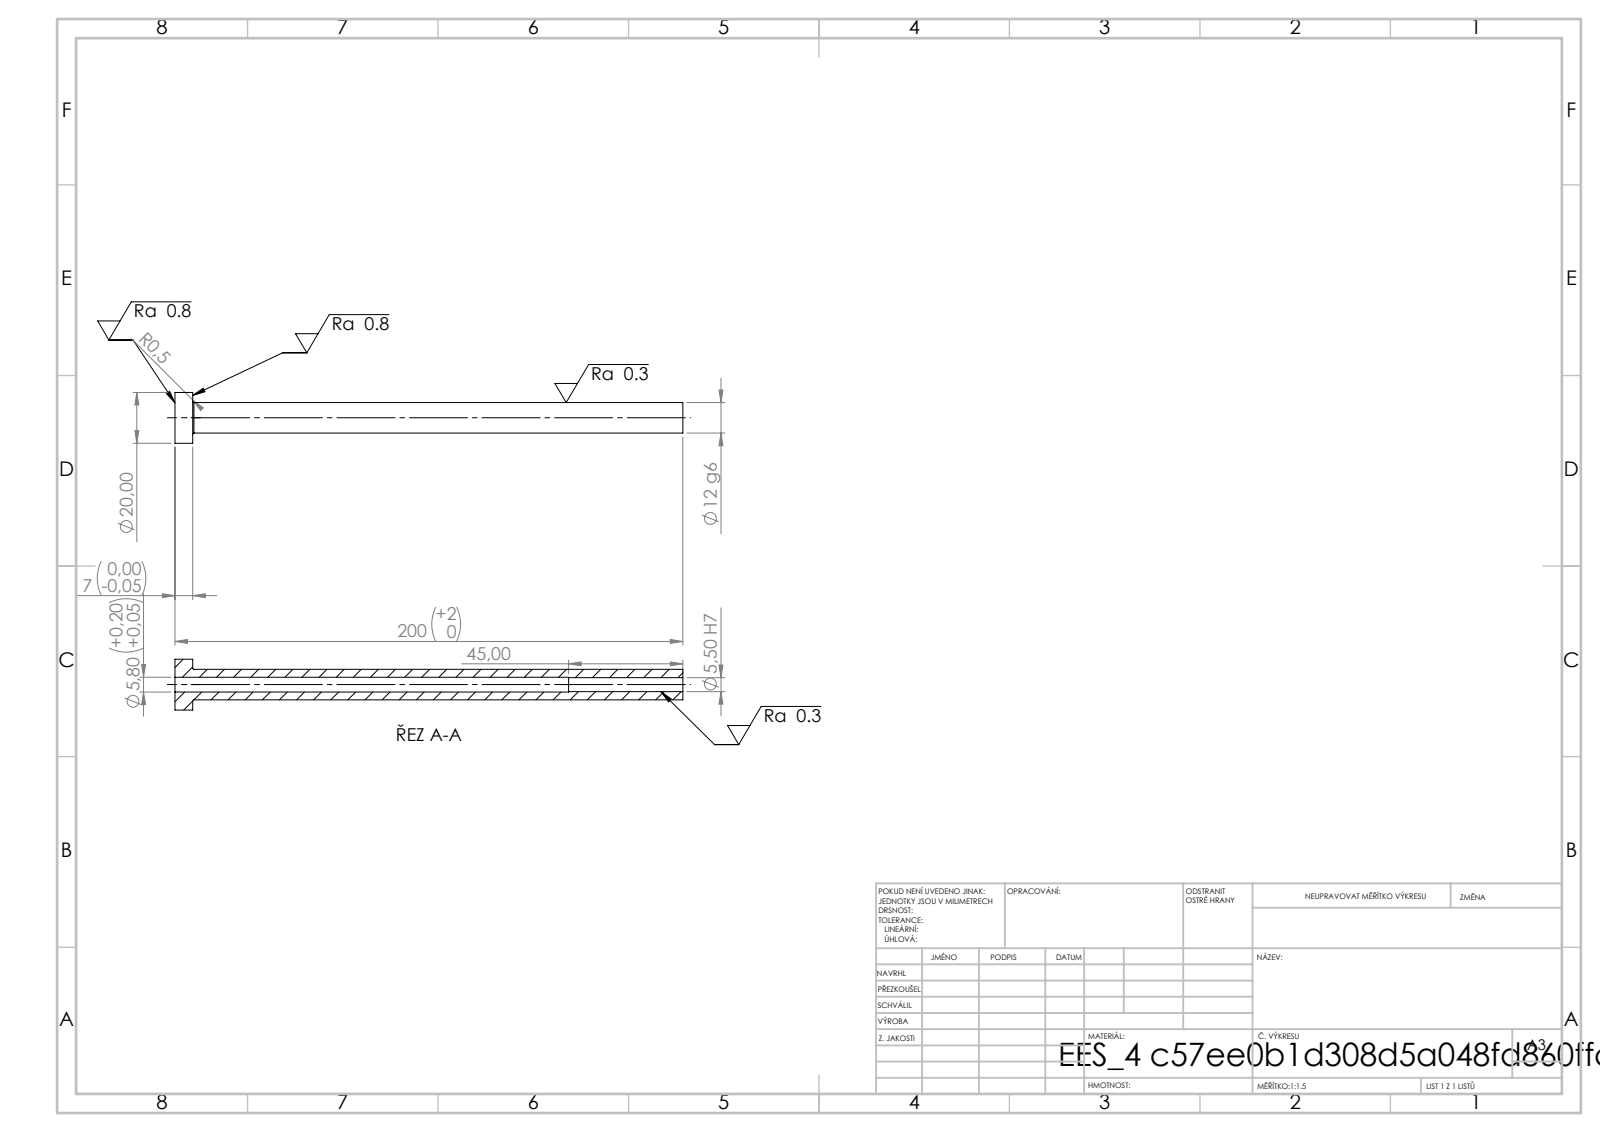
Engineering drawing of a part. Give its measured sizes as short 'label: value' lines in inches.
written by: SolidWorks 2019 (CONFIG_CONTROL_DESIGN)
unit: in
bodies: 1 solid, 14 faces (4 planar, 8 cylindrical, 2 other)
size: 7.874 × 0.787 × 0.787
volume: 1.151 in³; area: 18.43 in²
holes: 1× ⌀0.217, 1× ⌀0.228
bosses: 1× ⌀0.787, 1× ⌀0.472
face distances: 0.276, 7.874, 7.598, 6.102, 5.827, 1.772
